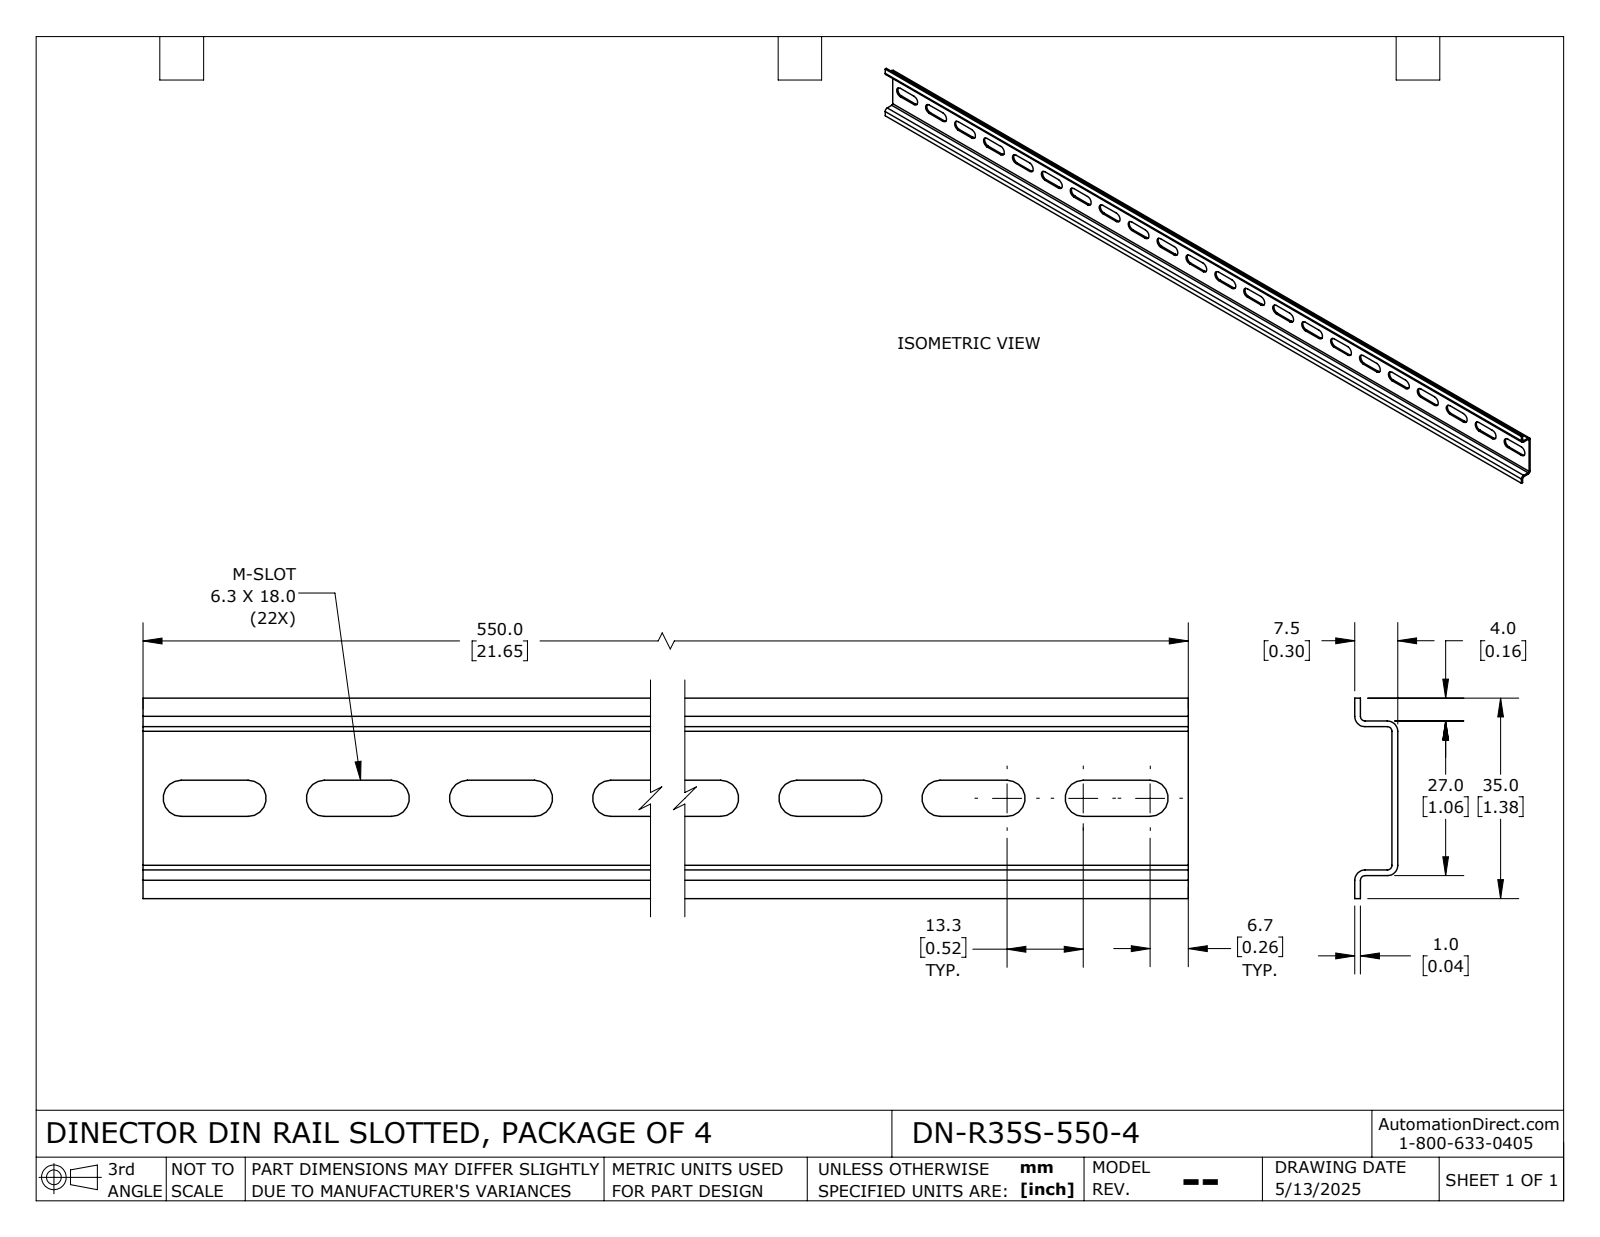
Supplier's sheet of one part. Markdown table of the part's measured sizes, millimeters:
| quantity | value |
| --- | --- |
| part name | DN-R35S-550-4_Default |
| STEP written by | SolidWorks 2024 (CONFIG_CONTROL_DESIGN) |
| units | millimeters |
| bodies | 1 solid, 110 faces (58 planar, 52 cylindrical, 0 other) |
| overall size | 550 × 35 × 7.5 |
| volume | 22 865 mm³ |
| surface area | 47 872 mm² |
| partial cylindrical surfaces (radius × count) | 3.15 × 44, 0.8 × 4, 1.8 × 4 |
| main face-to-face distances | 1, 6.5, 26, 7.5, 5.5, 27, 25, 4, 5, 30 |
